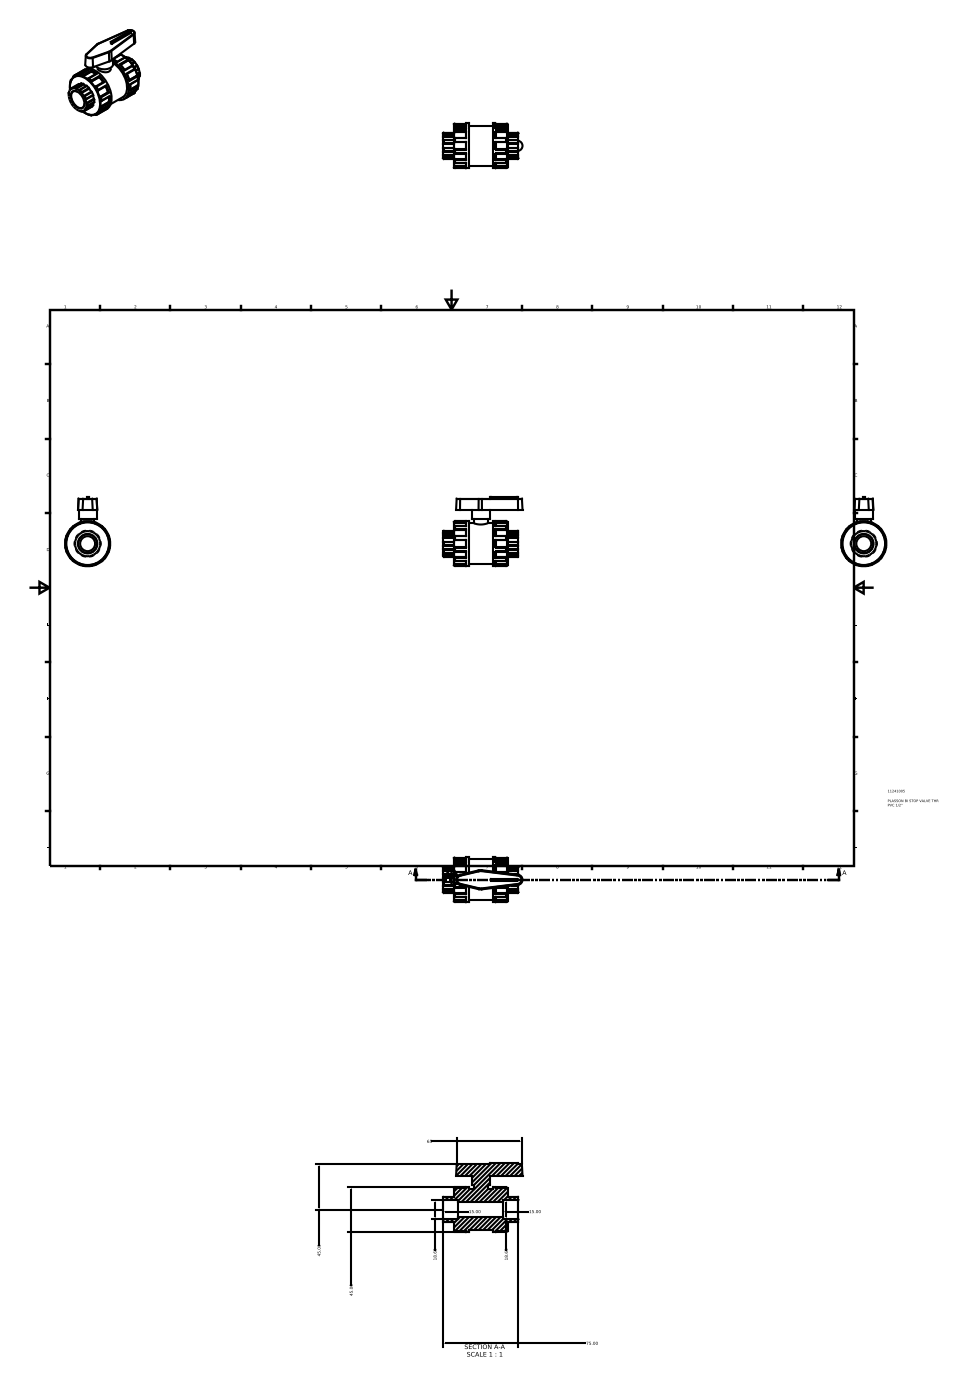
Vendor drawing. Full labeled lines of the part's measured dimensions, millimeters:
Part name (STEP PRODUCT): 11241005
STEP written by: Autodesk Inventor 2015 (AUTOMOTIVE_DESIGN)
Units: millimetres
Bodies: 1 solid, 434 faces (114 planar, 192 cylindrical, 128 other)
Overall size (bounding box): 79.09 × 68.85 × 45
Volume: 84 224 mm³ · Surface area: 20 387 mm²
Round holes (diameter × count): ⌀14.9 ×1, ⌀18.63 ×1
Round bosses / shafts (diameter × count): ⌀45 ×1, ⌀43.2 ×1, ⌀40.5 ×1, ⌀18 ×1, ⌀13.5 ×1
Partial cylindrical surfaces — rounded edges, fillets, slot ends (radius × count): R0.56 ×68, R0.37 ×4, R0.9 ×2, R12.48 ×1, R13.04 ×1
Main face-to-face distances: 54, 15, 11.25, 39, 10.5, 49.5, 25.5, 64.5, 24, 60
